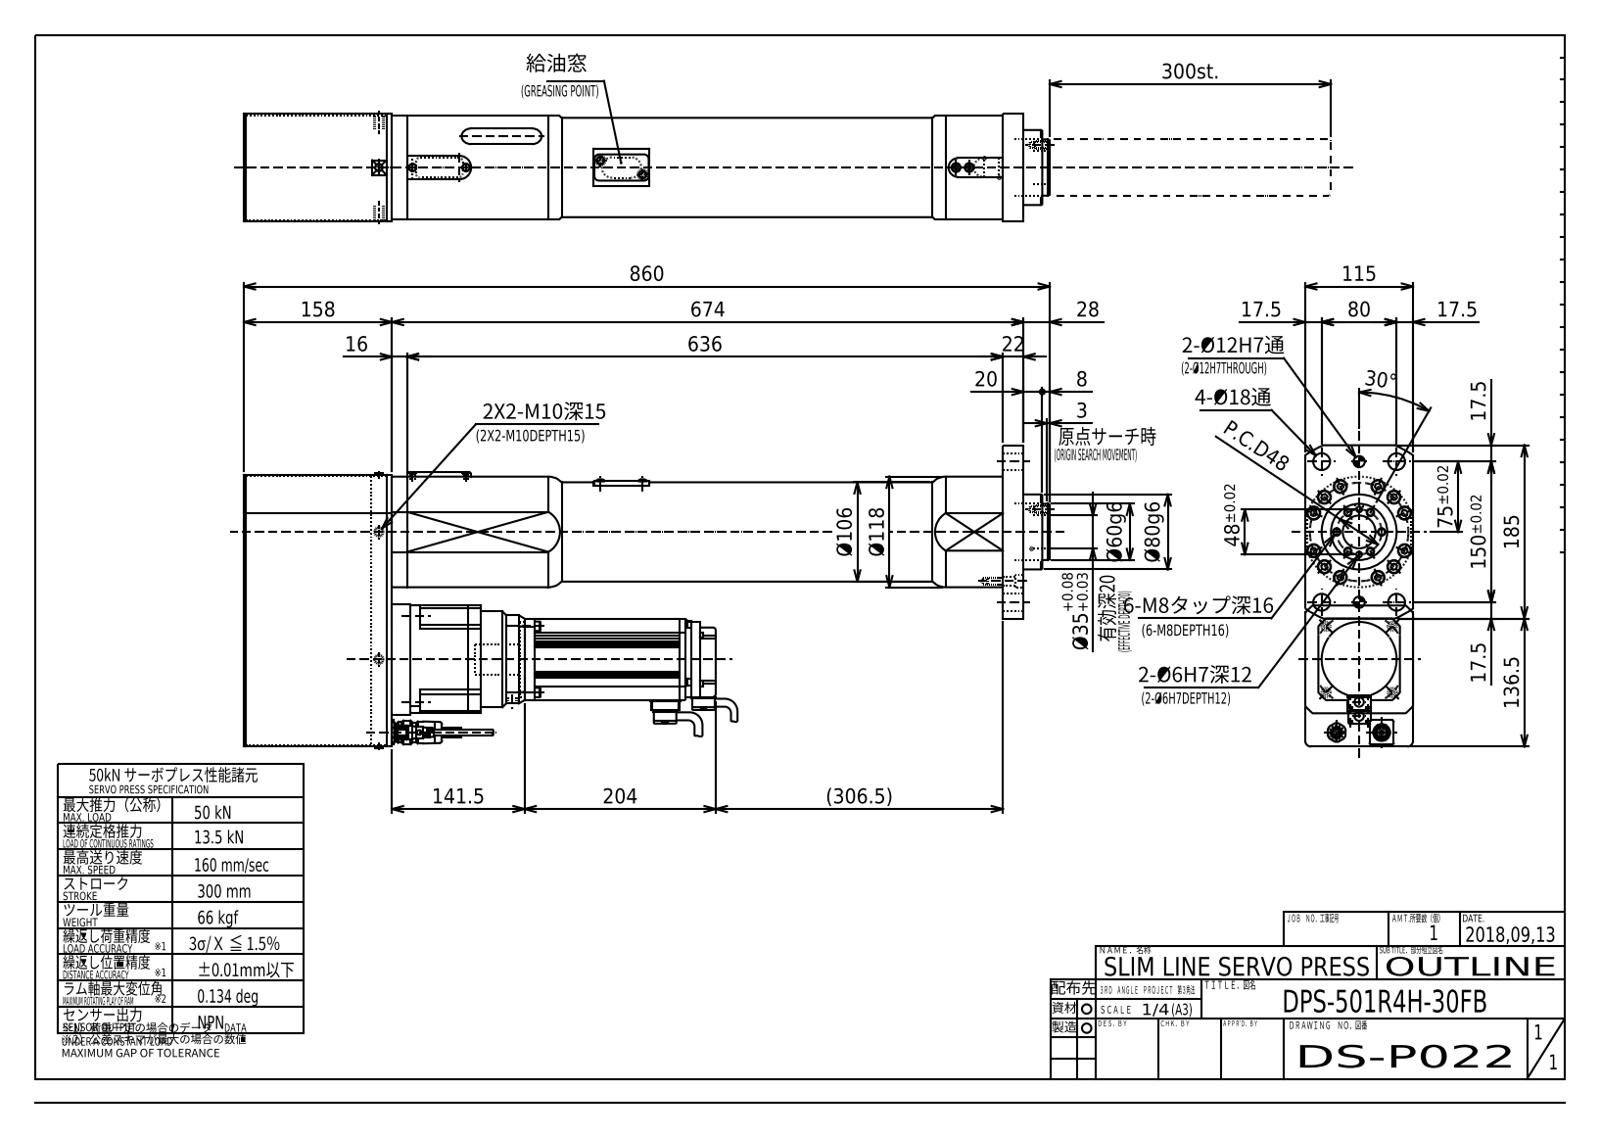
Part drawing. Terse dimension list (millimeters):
name: DPS-501R4H-30FB(DS-P022)_OUTLINE; DS-P022-02_OUTLINE
written by: Autodesk Inventor 2017 (AUTOMOTIVE_DESIGN)
unit: mm
bodies: 2 solids, 1438 faces (817 planar, 394 cylindrical, 227 other)
size: 860 × 323 × 118
volume: 14 200 000 mm³; area: 889 938 mm²
holes: 12× ⌀14, 8× ⌀6.65, 4× ⌀6.6, 4× ⌀18, 2× ⌀2.46, 2× ⌀6, 2× ⌀8, 2× ⌀9.5, 2× ⌀12, 1× ⌀4, 1× ⌀4.13, 1× ⌀8.5
bosses: 16× ⌀13, 10× ⌀6, 5× ⌀10, 4× ⌀8.8, 4× ⌀7.5, 4× ⌀7, 3× ⌀8, 2× ⌀80
rounds: 52× R1, 30× R2, 16× R0.3, 16× R4, 14× R4.25, 12× R5, 8× R0.5, 8× R3
face distances: 115, 14, 101, 2.5, 112.5, 11.5, 35.5, 87, 110, 29
hole spacings: 52.5, 74.24, 20.48, 40.18, 58.33, 87.3, 97, 102.97
